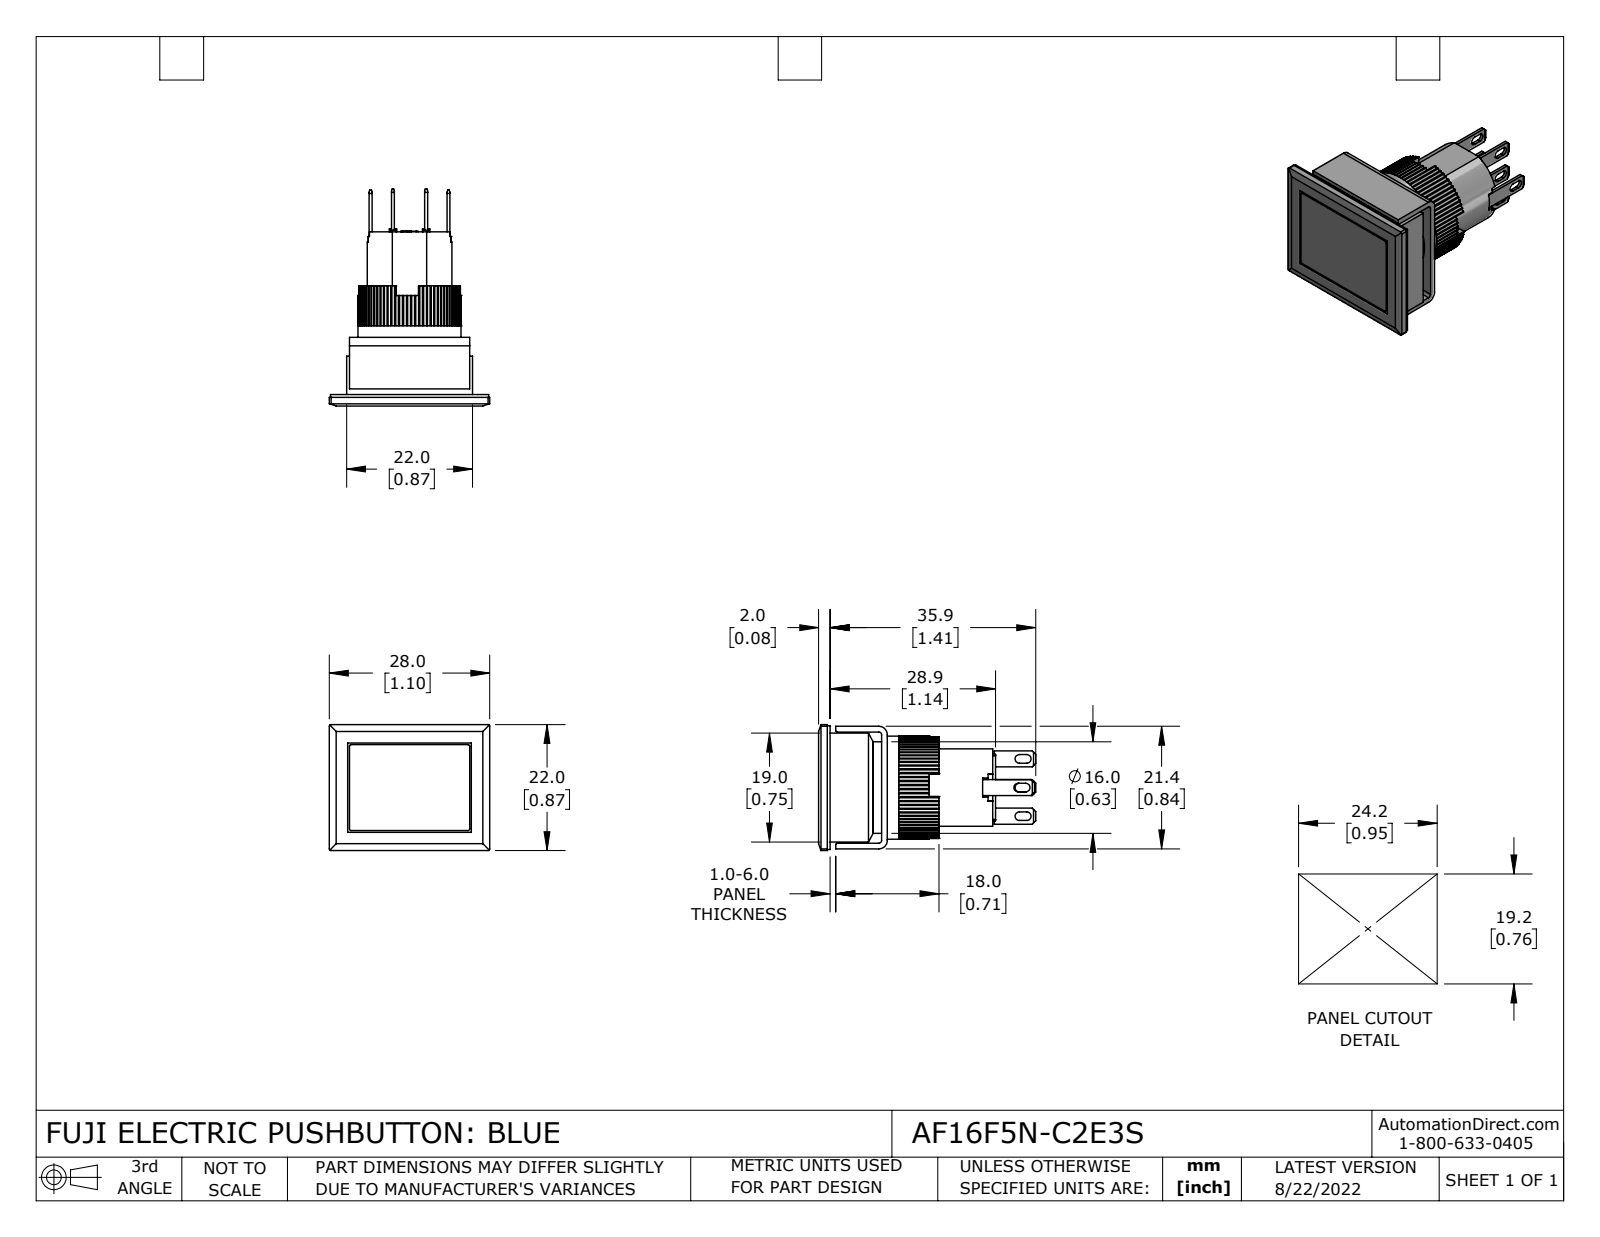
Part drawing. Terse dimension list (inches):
name: AF16F5N-C2E3S
written by: SolidWorks 2021 (CONFIG_CONTROL_DESIGN)
unit: in
bodies: 14 solids, 828 faces (644 planar, 182 cylindrical, 2 other)
size: 1.492 × 1.102 × 0.866
volume: 0.543 in³; area: 12.03 in²
holes: 1× ⌀0.039, 1× ⌀0.709
bosses: 1× ⌀0.63, 1× ⌀0.583
rounds: 80× R0.01, 12× R0.008, 8× R0.012, 8× R0.03, 2× R0.02, 2× R0.059
face distances: 0.374, 0.059, 0.02, 0.142, 0.039, 0.315, 0.232, 0.083, 0.079, 0.756
